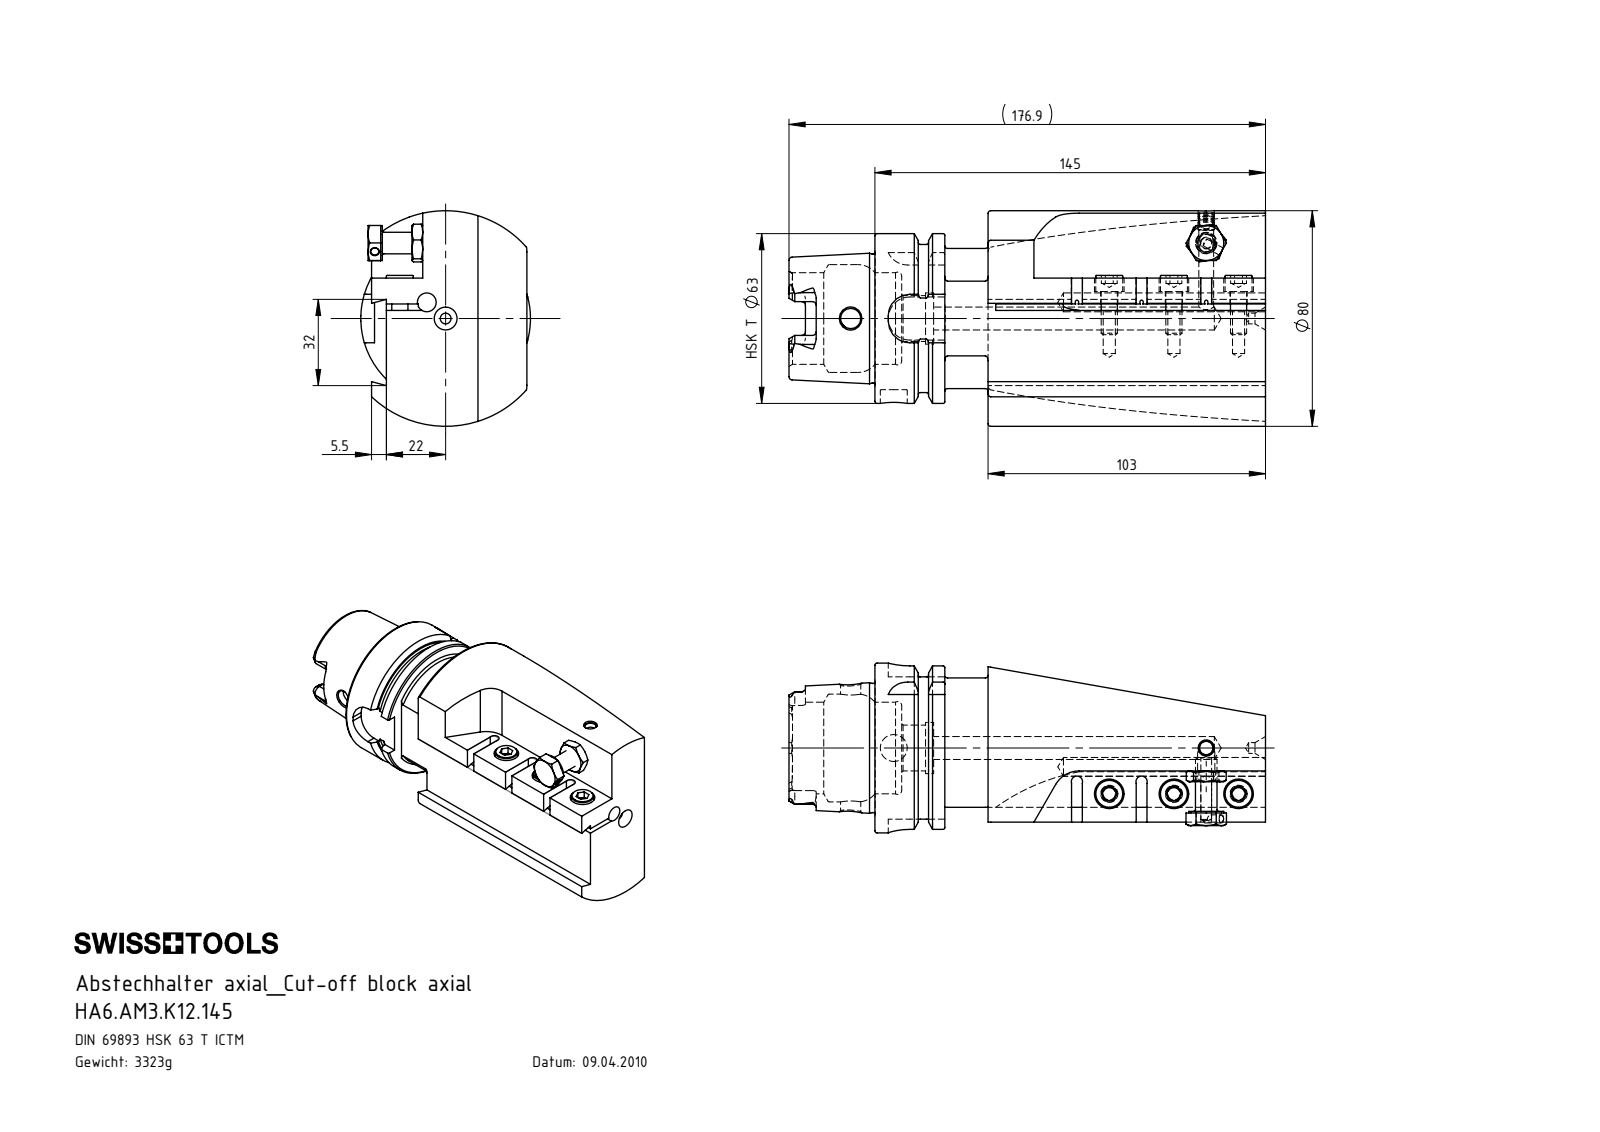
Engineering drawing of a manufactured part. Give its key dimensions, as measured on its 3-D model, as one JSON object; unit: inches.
{"part_name": "HA6.AM3.K12.145; KVT_MB_600_060; ISO 4035 - M8_PreviewCfg; AM3-ER1.001.020_PreviewCfg (+2 more)", "step_written_by": "SolidWorks 2011 (AUTOMOTIVE_DESIGN)", "units": "inches", "bodies": {"solids": 8, "faces": 434, "planar": 147, "cylindrical": 107, "other": 180}, "overall_size": [6.965, 3.15, 2.48], "volume_in3": 25.8, "surface_area_in2": 100.9, "round_holes": [[0.252, 4], [0.177, 3], [0.433, 3], [0.157, 2], [0.276, 2], [0.118, 1], [0.197, 1], [0.217, 1], [0.236, 1], [0.295, 1], [0.331, 1], [0.394, 1]], "round_bosses_or_shafts": [[0.236, 4], [0.394, 3], [2.48, 1], [2.163, 1], [2.047, 1], [1.887, 1], [0.512, 1], [0.315, 1]], "partial_cylinders_radius": [[0.055, 4], [0.315, 4], [0.083, 3], [0.113, 2], [0.394, 2], [1.575, 1], [3.051, 1]], "face_to_face_distances": [0.531, 0.748, 0.217, 4.055, 0.472, 1.654, 5.709, 0.079, 0.394, 0.197], "hole_center_spacings": [0.822, 0.945, 0.363, 1.569, 1.89, 3.221, 4.15, 4.567]}
